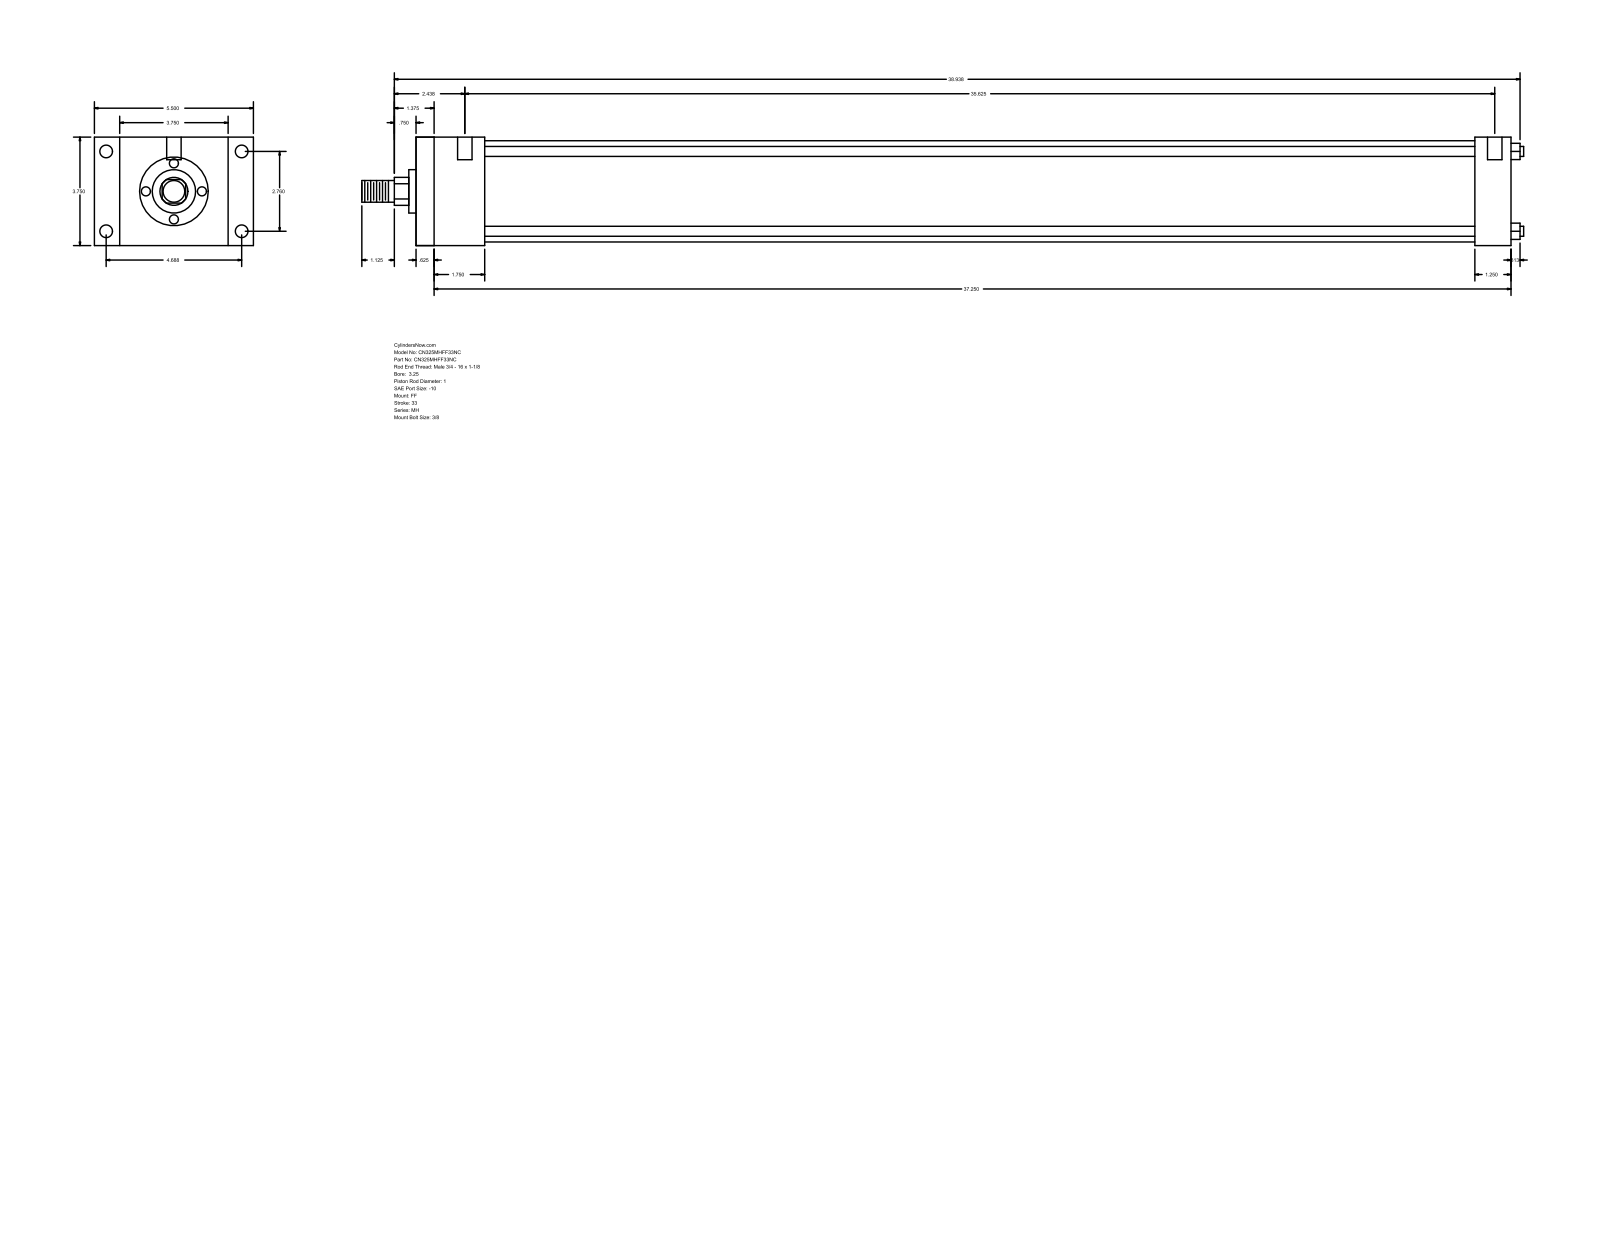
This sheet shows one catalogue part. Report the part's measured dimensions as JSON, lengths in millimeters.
{"part_name": "MH_FF__0325_1", "step_written_by": "GSSL Pune (CONFIG_CONTROL_DESIGN)", "units": "millimeters", "bodies": {"solids": 0, "faces": 92, "planar": 64, "cylindrical": 28, "other": 0}, "overall_size": [1020.76, 139.7, 95.25], "round_holes": [[5.56, 4], [11.13, 4], [12.7, 2]], "round_bosses_or_shafts": [[8.76, 4], [88.9, 1], [38.1, 1], [25.4, 1], [19.05, 1]], "partial_cylinders_radius": [[12.29, 1]], "face_to_face_distances": [95.24, 962.03, 15.87, 946.16, 22.23, 117.47, 930.28, 914.41, 31.75, 60.33], "hole_center_spacings": [70.1, 119.06, 138.16, 911.22, 1.58, 4.76, 904.88, 906.46]}
